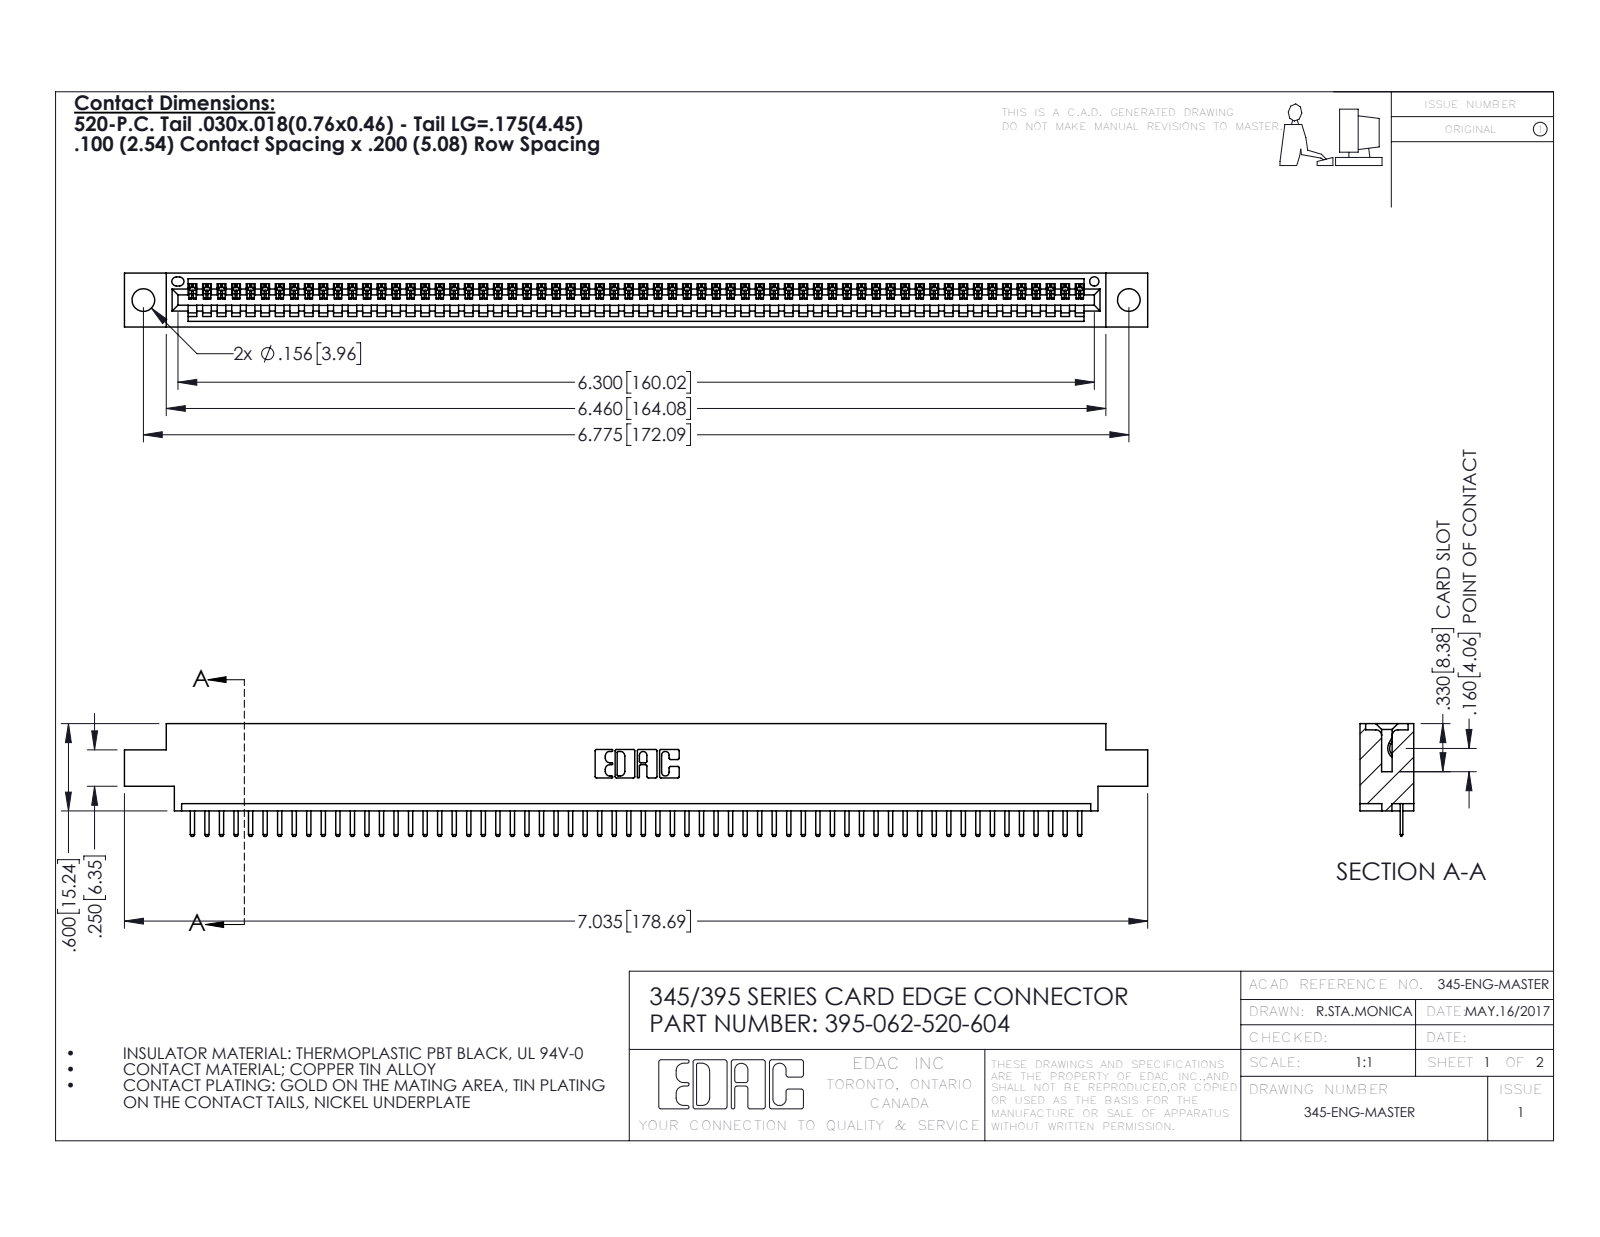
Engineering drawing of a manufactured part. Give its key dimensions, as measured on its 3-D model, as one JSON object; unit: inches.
{"part_name": "345-292-001_345-293-120; 395-062-520-604; 345 Part_0.170 Offset - 0.156 Dia-TH", "step_written_by": "SolidWorks 2016 (CONFIG_CONTROL_DESIGN)", "units": "inches", "bodies": {"solids": 63, "faces": 3974, "planar": 2688, "cylindrical": 1286, "other": 0}, "overall_size": [7.035, 0.775, 0.37], "volume_in3": 1.023, "surface_area_in2": 33.93, "round_holes": [[0.156, 2], [0.064, 1]], "partial_cylinders_radius": [[0.01, 126], [0.006, 124], [0.01, 22], [0.007, 6], [0.031, 6], [0.026, 3], [0.031, 2], [0.04, 2]], "face_to_face_distances": [0.298, 0.072, 0.37, 0.2, 0.098, 0.272, 0.025, 0.225, 0.072, 0.175], "hole_center_spacings": [0.27, 6.539, 6.775]}
